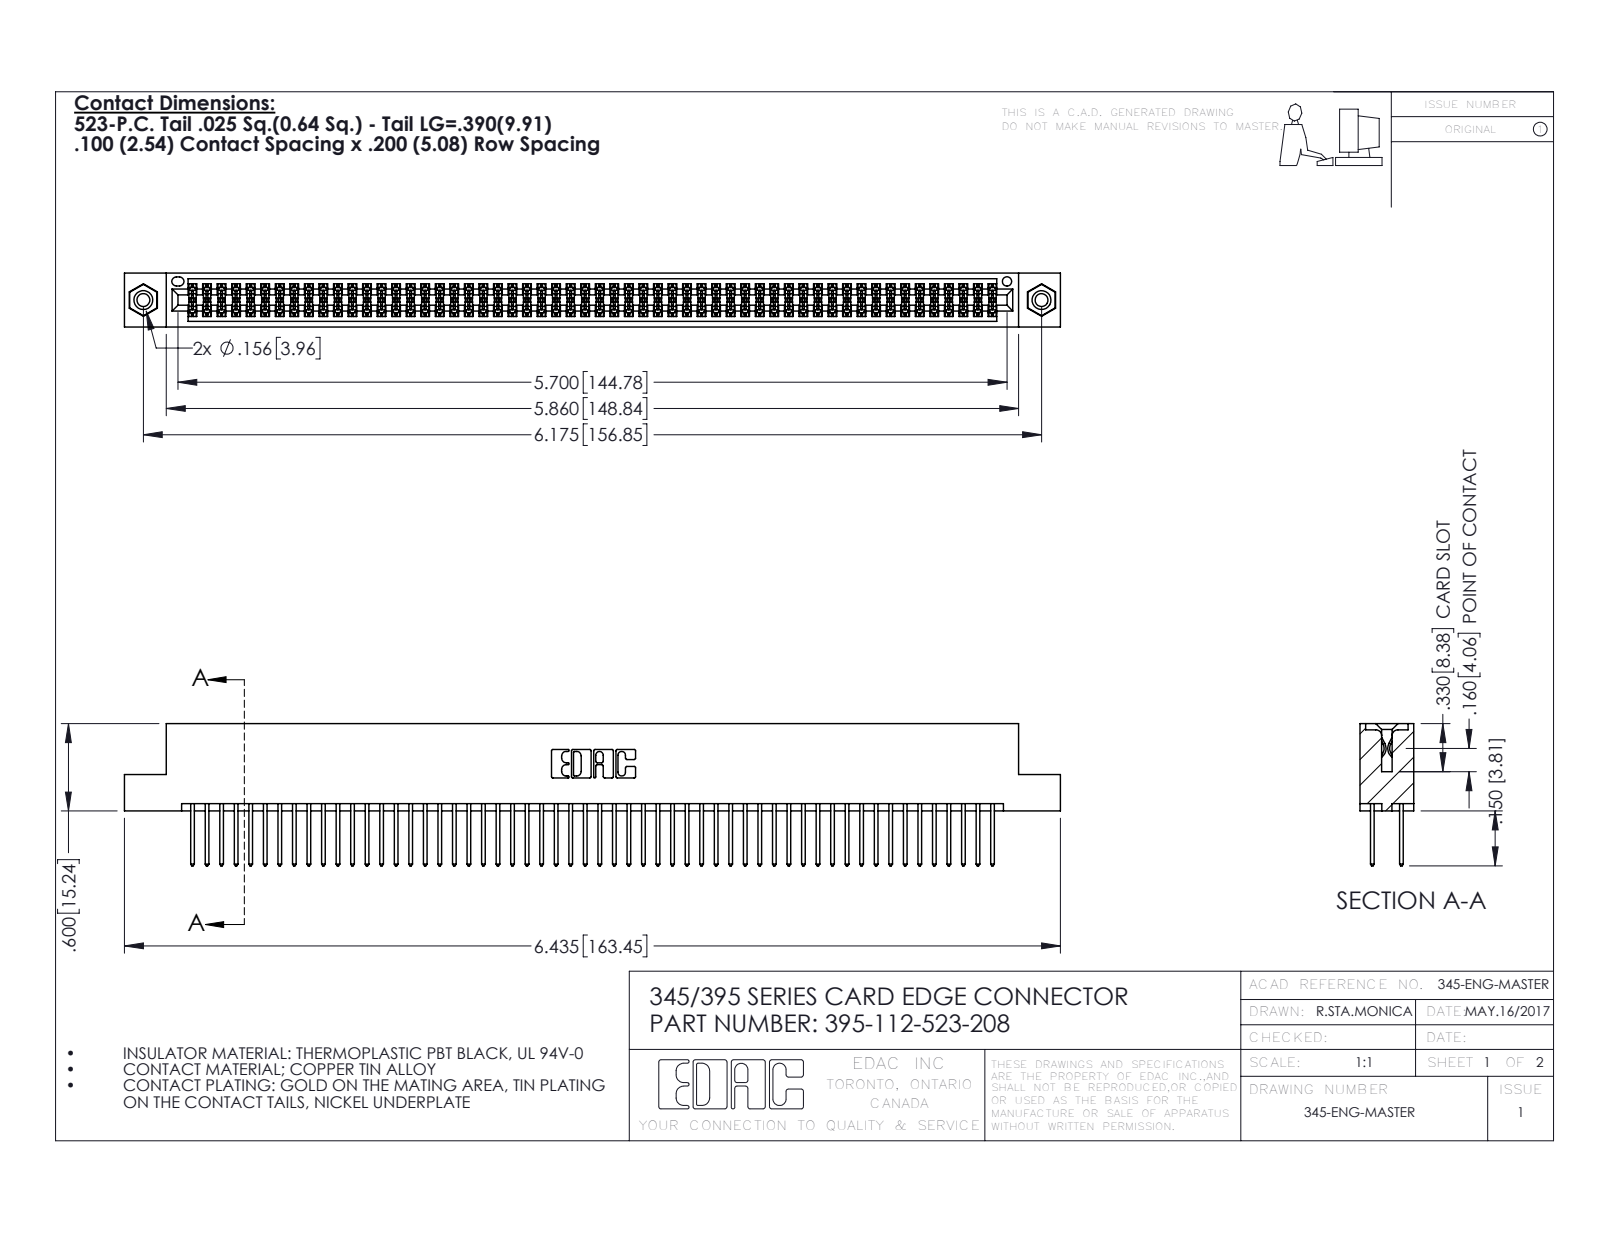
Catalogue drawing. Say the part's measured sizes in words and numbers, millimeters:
The part is named "345-250-001_345-250-003-102; 345 Part_Flush Mounting Lugs - 0.156 Dia-TI; 345-292-001_345-293-123; 395-112-523-208". Its 3-D file was written by "SolidWorks 2016 (CONFIG_CONTROL_DESIGN)". It is 115 solids with 5786 faces: 3808 planar, 1962 cylindrical and 16 other. Overall it measures 163.4 by 24.8 by 9.4 millimeters. Its volume is 16 200 cubic millimeters and its surface area 25 300 square millimeters. Round holes: 2 of diameter 2.3, 2 of diameter 3.2, 2 of diameter 4, 1 of diameter 1.6. Round bosses or shafts: 2 of diameter 3.9. Partial cylindrical surfaces (rounded edges, fillets, slot ends): 168 of radius 0.2, 112 of radius 0.3, 22 of radius 0.3, 6 of radius 0.2, 6 of radius 0.8, 3 of radius 0.7, 2 of radius 0.4, 2 of radius 0.5. The main face-to-face distances are 1.8, 7.6, 5.1, 2.5, 6.9, 0.6, 9.4, 5.7, 4.4, 3.8. The hole center spacings are 6.9, 150.9, 156.8.
